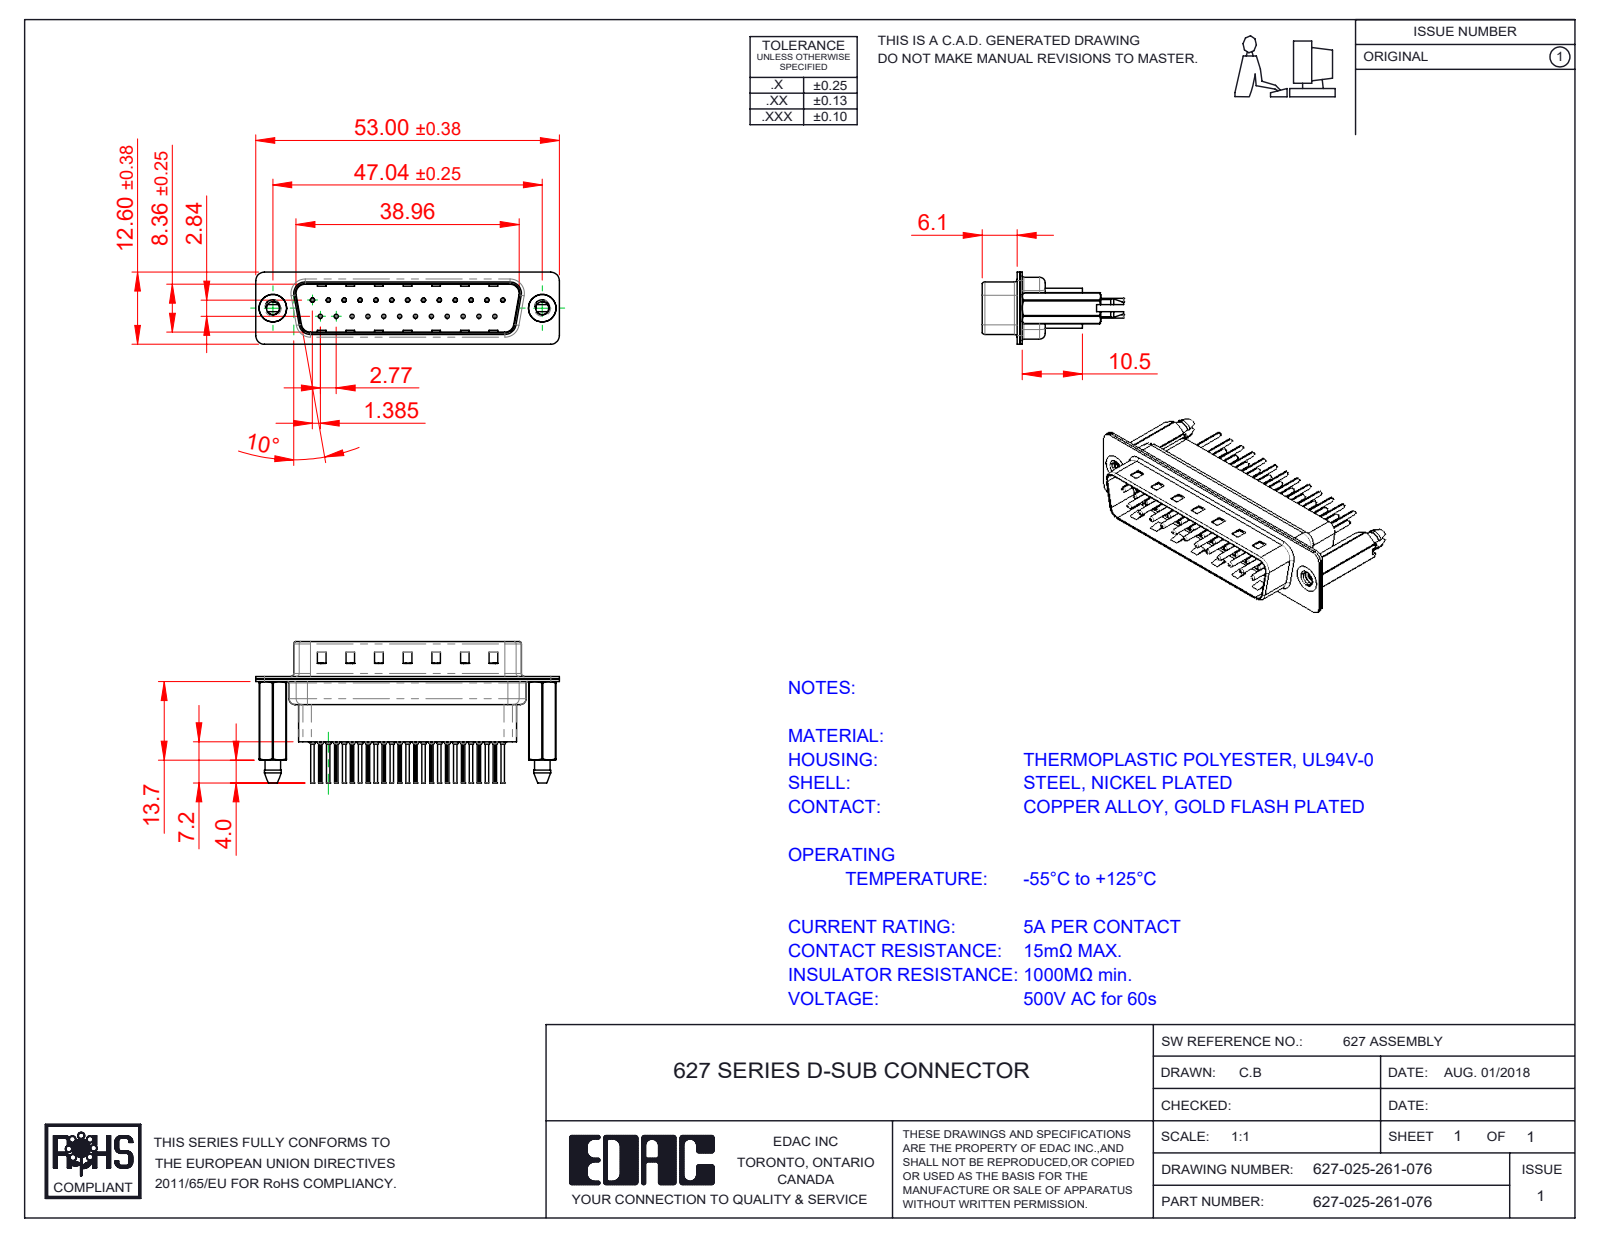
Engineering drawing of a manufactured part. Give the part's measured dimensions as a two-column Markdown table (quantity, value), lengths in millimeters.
| quantity | value |
| --- | --- |
| part name | 627 Contact Row 1_61; 627 Shell Rear_25 Contacts; 627 Shell Front_25 Contacts; 627 Housing_25 HP (+3 more) |
| STEP written by | SolidWorks 2020 (CONFIG_CONTROL_DESIGN) |
| units | millimeters |
| bodies | 30 solids, 2934 faces (803 planar, 1128 cylindrical, 1003 other) |
| overall size | 53 × 24.6 × 12.6 |
| volume | 4 164 mm³ |
| surface area | 10 770 mm² |
| round holes (diameter × count) | 0.2 × 25, 0.35 × 25, 1.1 × 25, 1.6 × 25, 2.26 × 2, 4 × 2, 4.8 × 2 |
| round bosses / shafts (diameter × count) | 2 × 25, 1.5 × 25, 0.75 × 25, 0.6 × 25, 4.9 × 2 |
| partial cylindrical surfaces (radius × count) | 0.1 × 50, 1.5 × 18, 2 × 12, 1.6 × 10, 0.5 × 8, 0.25 × 4, 0.6 × 4, 0.65 × 4 |
| main face-to-face distances | 0.4, 0.45, 0.82, 9.58, 0.68, 7.68, 1.5, 0.9, 1.08, 8.08 |
| hole center spacings | 3.16, 8.31, 2.77, 5.54, 11.08, 16.62, 5.03, 5.04 |
